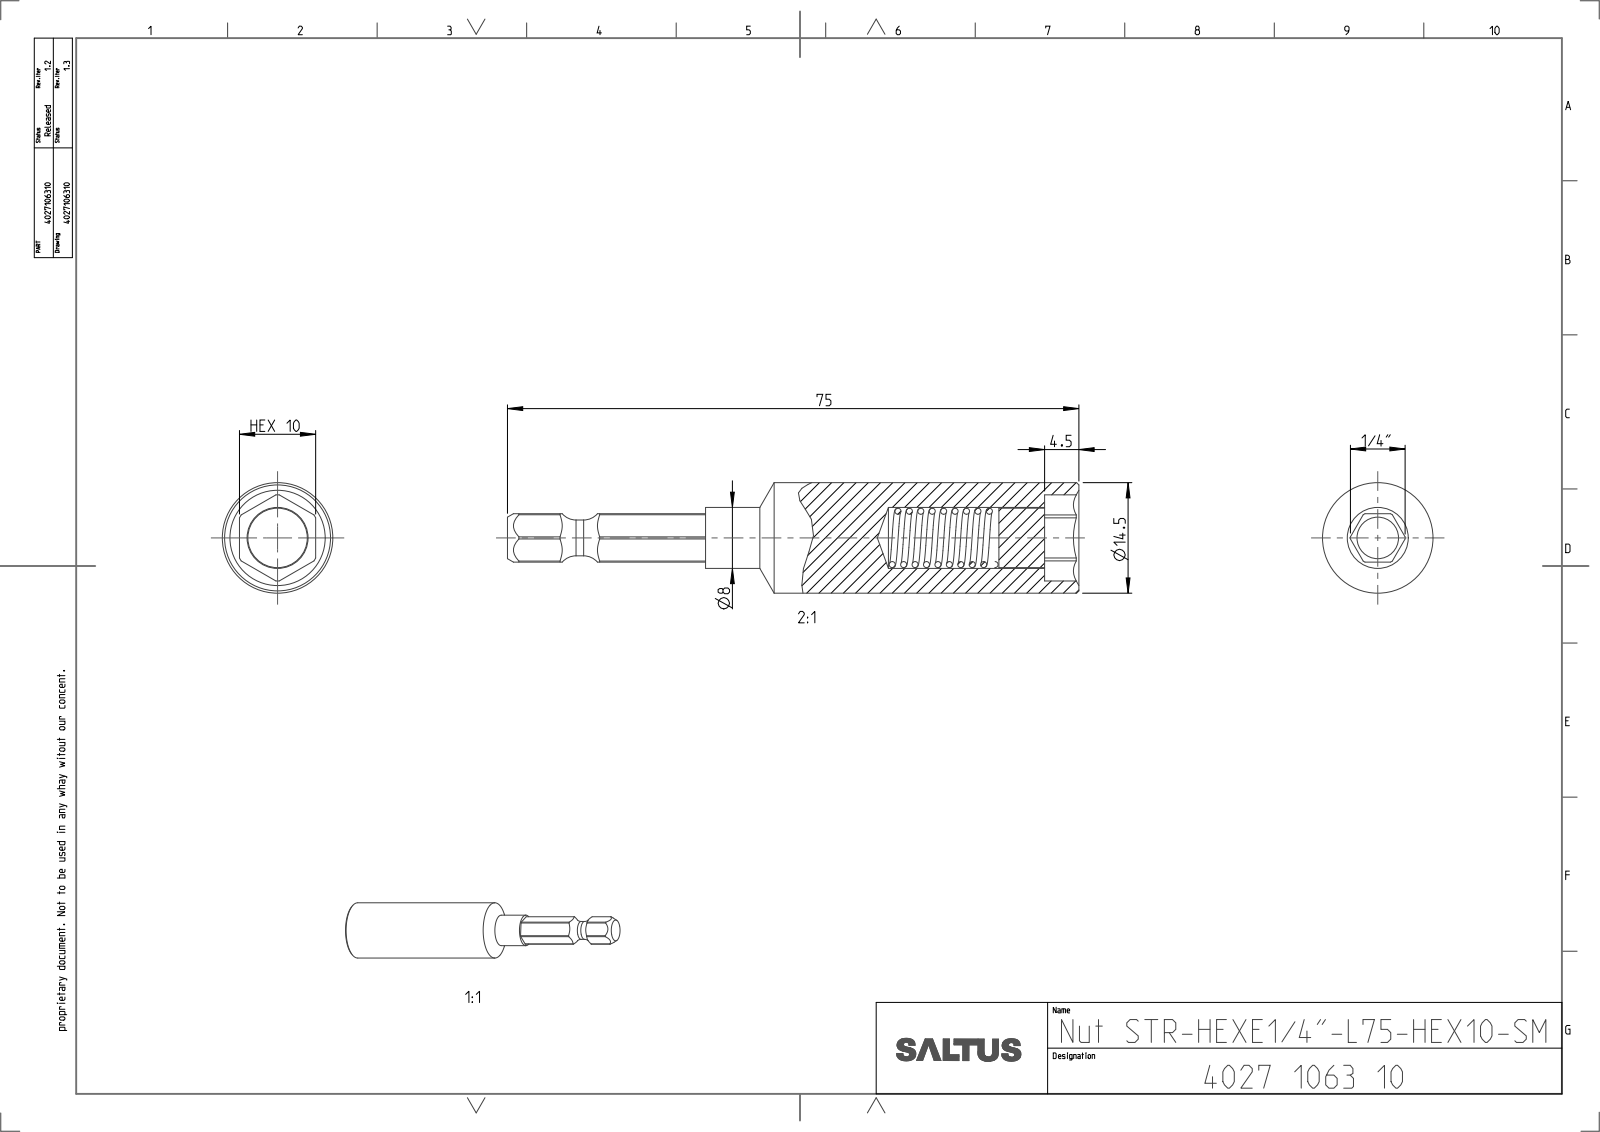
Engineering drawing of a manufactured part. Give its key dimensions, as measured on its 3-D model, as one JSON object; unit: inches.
{"part_name": "4027106310", "step_written_by": "CREO PARAMETRIC BY PTC INC, 2022414 (CONFIG_CONTROL_DESIGN)", "units": "inches", "bodies": {"solids": 3, "faces": 74, "planar": 26, "cylindrical": 28, "other": 20}, "overall_size": [2.953, 0.571, 0.571], "volume_in3": 0.422, "surface_area_in2": 6.637, "round_holes": [[0.315, 1]], "round_bosses_or_shafts": [[0.571, 1], [0.307, 1], [0.185, 1]], "partial_cylinders_radius": [[0.141, 1], [0.222, 1]], "face_to_face_distances": [0.25, 0.25, 0.394, 0.236, 0.413, 0.177, 2.539, 2.776, 2.953, 1.024]}
